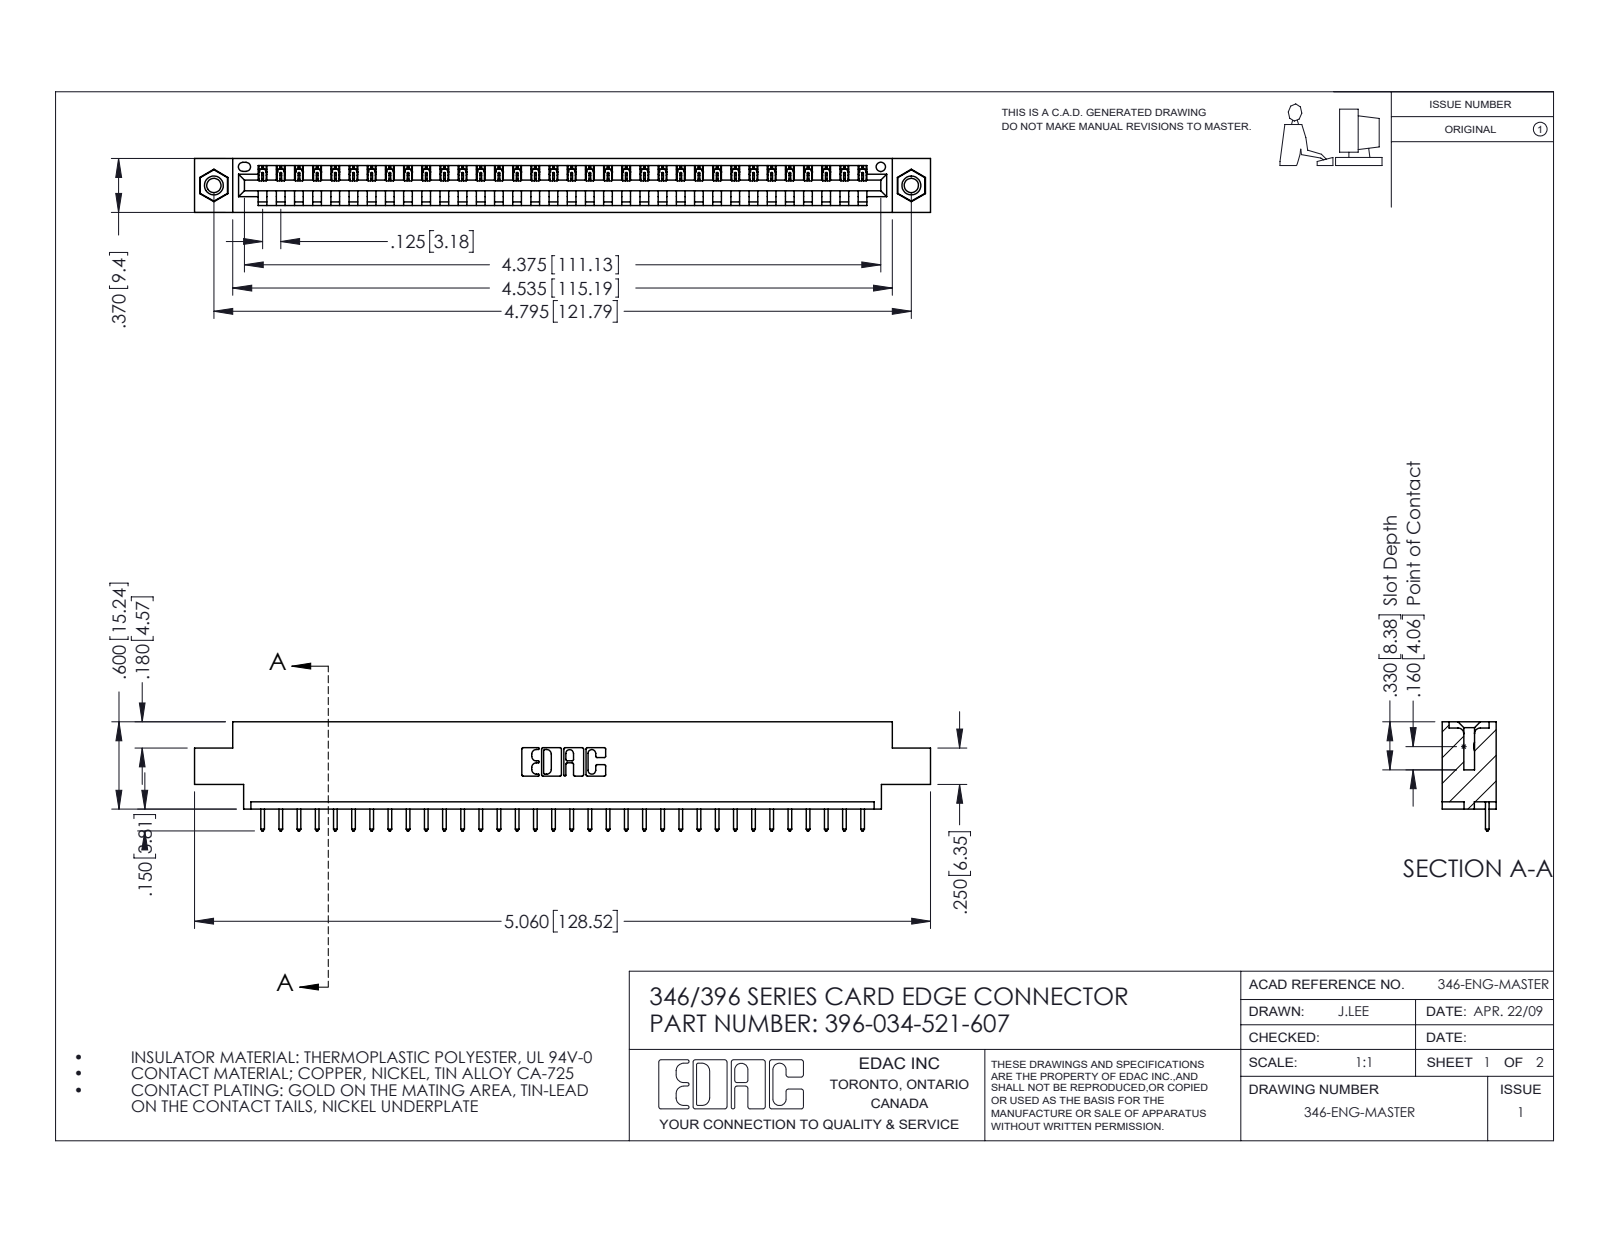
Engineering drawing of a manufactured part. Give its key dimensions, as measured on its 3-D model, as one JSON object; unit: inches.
{"part_name": "346 Part_0.170 Offset - 0.156 Dia-TI; 396-034-521-607; 345-250-001_345-250-005-103; 345-292-001_345-293-121", "step_written_by": "SolidWorks 2016 (CONFIG_CONTROL_DESIGN)", "units": "inches", "bodies": {"solids": 37, "faces": 2158, "planar": 1472, "cylindrical": 670, "other": 16}, "overall_size": [5.06, 0.75, 0.37], "volume_in3": 0.731, "surface_area_in2": 22.79, "round_holes": [[0.098, 2], [0.125, 2], [0.156, 2], [0.064, 1]], "round_bosses_or_shafts": [[0.155, 2]], "partial_cylinders_radius": [[0.006, 68], [0.01, 68], [0.01, 22], [0.007, 6], [0.031, 6], [0.026, 3], [0.031, 2], [0.04, 2]], "face_to_face_distances": [0.048, 0.322, 0.37, 0.25, 0.072, 0.298, 0.025, 0.222, 0.148, 0.1], "hole_center_spacings": [0.246, 4.587, 4.795]}
